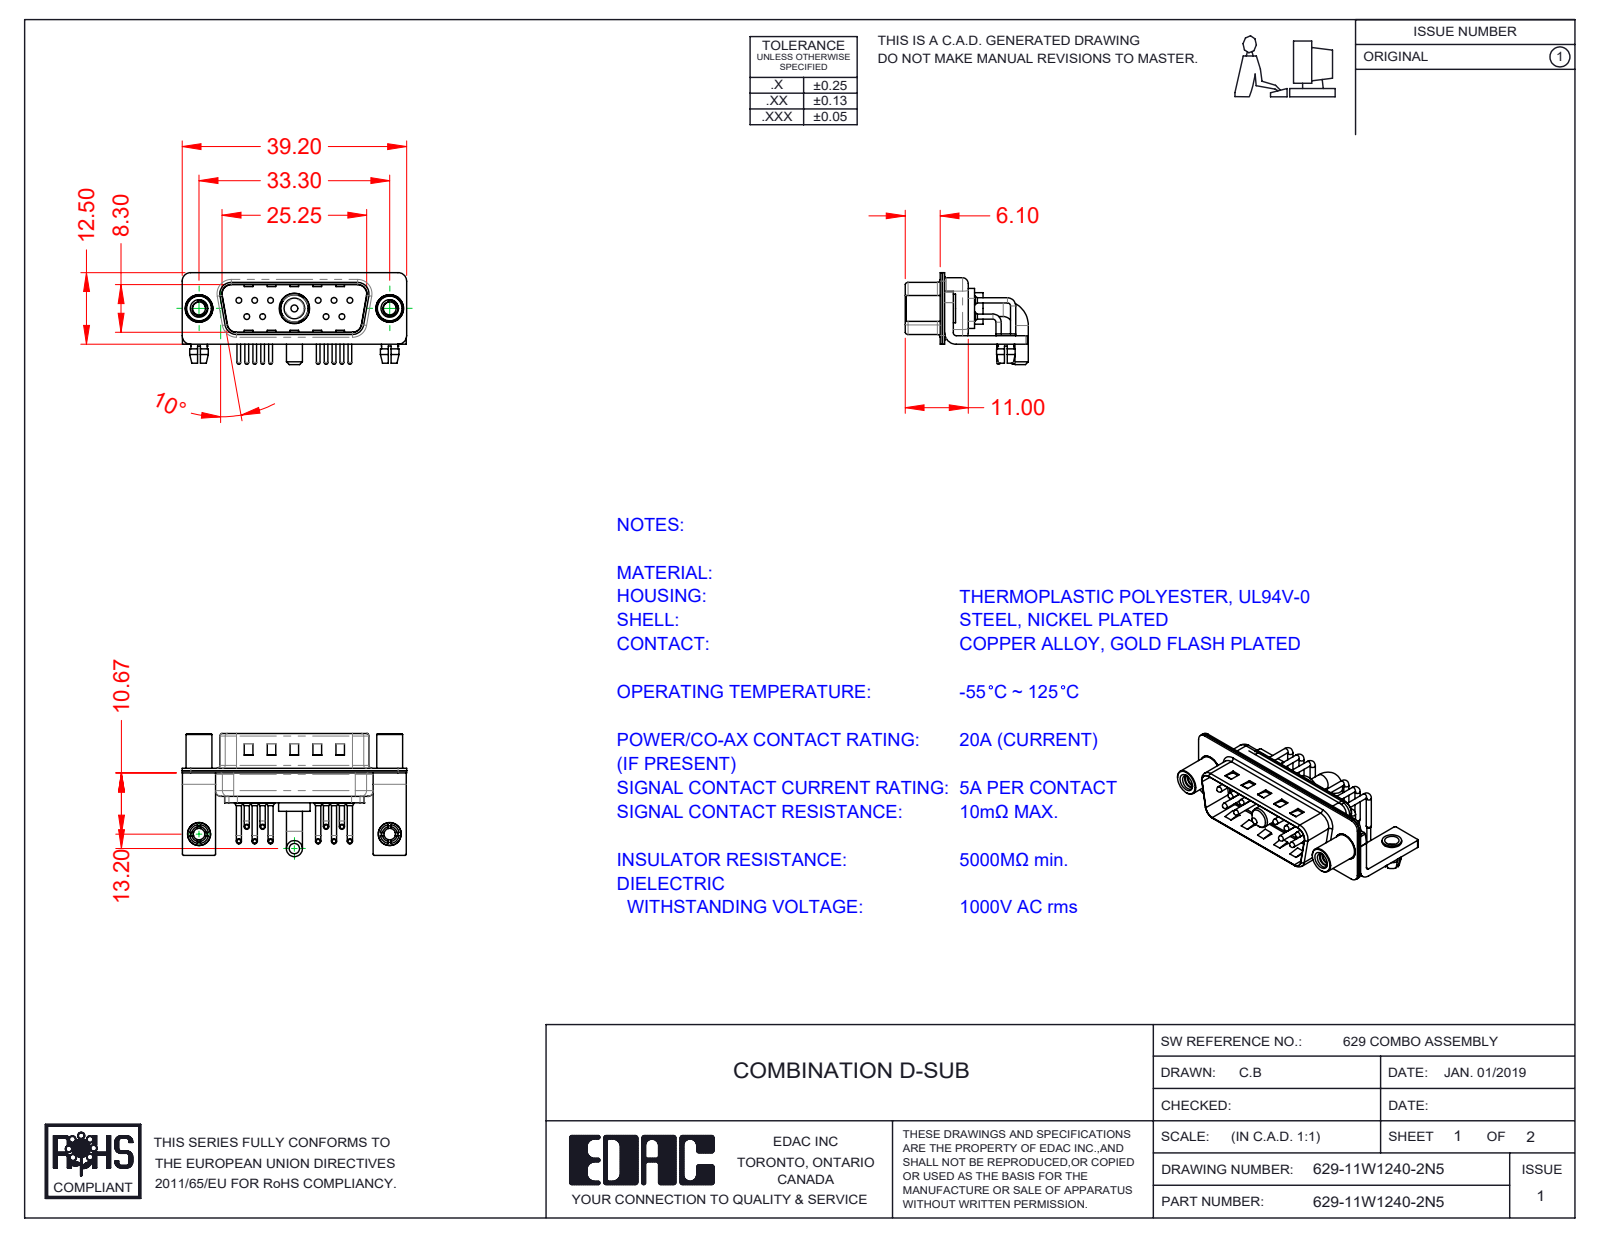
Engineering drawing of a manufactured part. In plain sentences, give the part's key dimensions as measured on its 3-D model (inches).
The part is named "629Combo Shell Rear_15 Contacts; 629Combo Contact Row 2; 629Combo Stabilizer Bracket; 629Combo Shell Front_15 Contacts (+6 more)". Its 3-D file was written by "SolidWorks 2020 (CONFIG_CONTROL_DESIGN)". It is 21 solids with 1676 faces: 868 planar, 610 cylindrical and 198 other. Overall it measures 1.543 by 0.846 by 0.632 inches. Its volume is 0.152 cubic inches and its surface area 9.855 square inches. Round holes: 12 of diameter 0.079, 10 of diameter 0.03, 10 of diameter 0.063, 2 of diameter 0.089, 2 of diameter 0.098, 2 of diameter 0.126, 2 of diameter 0.157, 2 of diameter 0.189, 1 of diameter 0.191, 1 of diameter 0.209. Round bosses or shafts: 20 of diameter 0.035, 10 of diameter 0.059, 10 of diameter 0.039, 10 of diameter 0.026, 2 of diameter 0.197, 2 of diameter 0.193, 2 of diameter 0.177, 2 of diameter 0.157. Partial cylindrical surfaces (rounded edges, fillets, slot ends): 16 of radius 0.01, 16 of radius 0.059, 13 of radius 0.079, 10 of radius 0.04, 9 of radius 0.02, 8 of radius 0.063, 7 of radius 0.039, 4 of radius 0.024. The main face-to-face distances are 0.016, 0.031, 0.059, 0.374, 0.358, 0.343, 0.39, 0.024, 0.075, 0.03. The hole center spacings are 0.124, 0.109, 0.545, 0.436, 0.654, 0.198, 0.198, 0.218.
